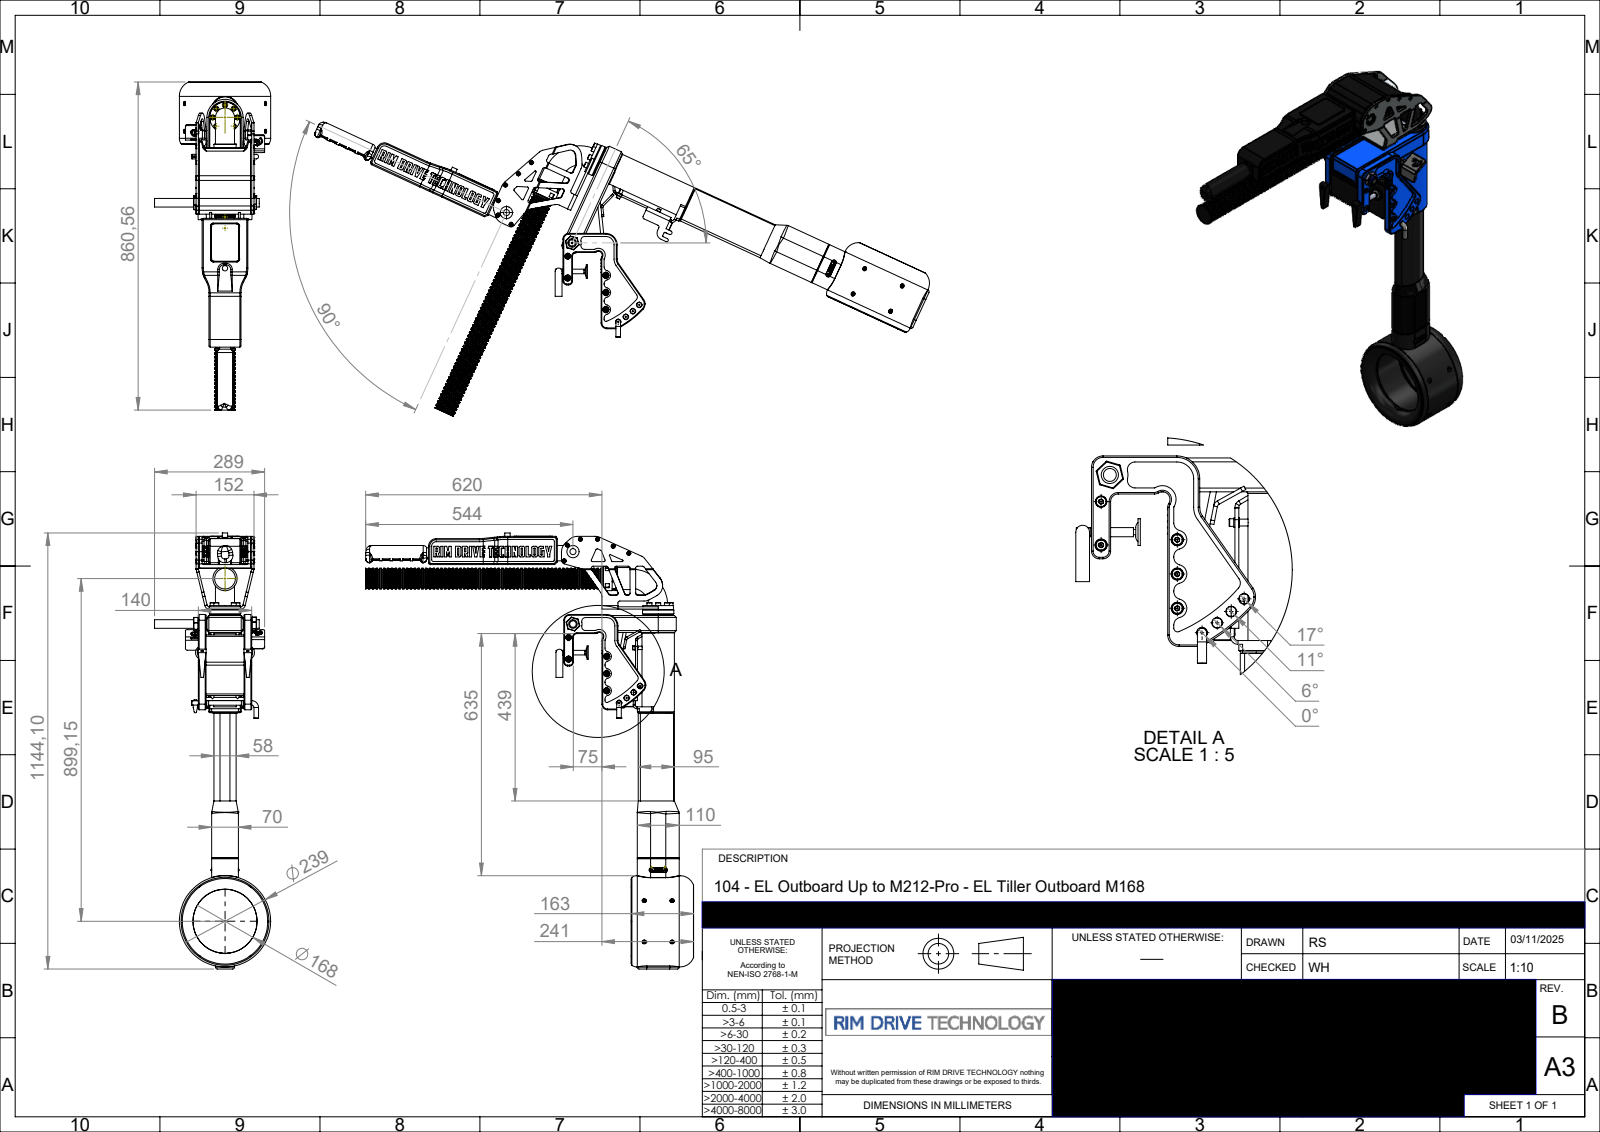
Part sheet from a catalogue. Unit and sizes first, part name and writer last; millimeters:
Units: millimetres
Overall size (bounding box): 1144.1 × 860.55 × 304.74
Round holes (diameter × count): ⌀5 ×5, ⌀15 ×5, ⌀5.5 ×4, ⌀13 ×4, ⌀3.5 ×2, ⌀6.1 ×2, ⌀6.4 ×2, ⌀4 ×1, ⌀17 ×1, ⌀32 ×1, ⌀85 ×1, ⌀168 ×1
Round bosses / shafts (diameter × count): ⌀13 ×13, ⌀9.64 ×10, ⌀12 ×7, ⌀10 ×4, ⌀5 ×4, ⌀8.1 ×3, ⌀35 ×2, ⌀6.95 ×2
Partial cylindrical surfaces — rounded edges, fillets, slot ends (radius × count): R3 ×60, R5 ×48, R0.5 ×45, R10 ×34, R2 ×26, R1 ×25, R6 ×12, R20 ×9
Main face-to-face distances: 6, 10, 20, 5, 120, 110, 15, 100, 95, 12.5
Hole centre spacings: 239.77, 23.7, 45, 47.35, 61.28, 73, 102.09, 110.63
Volume: 15 020 000 mm³ · Surface area: 1 383 000 mm²
Bodies: 1 solid, 4103 faces (2104 planar, 795 cylindrical, 1204 other)
Part name (STEP PRODUCT): P-104-250-rev-B-168
STEP written by: SolidWorks 2024 (AUTOMOTIVE_DESIGN)
